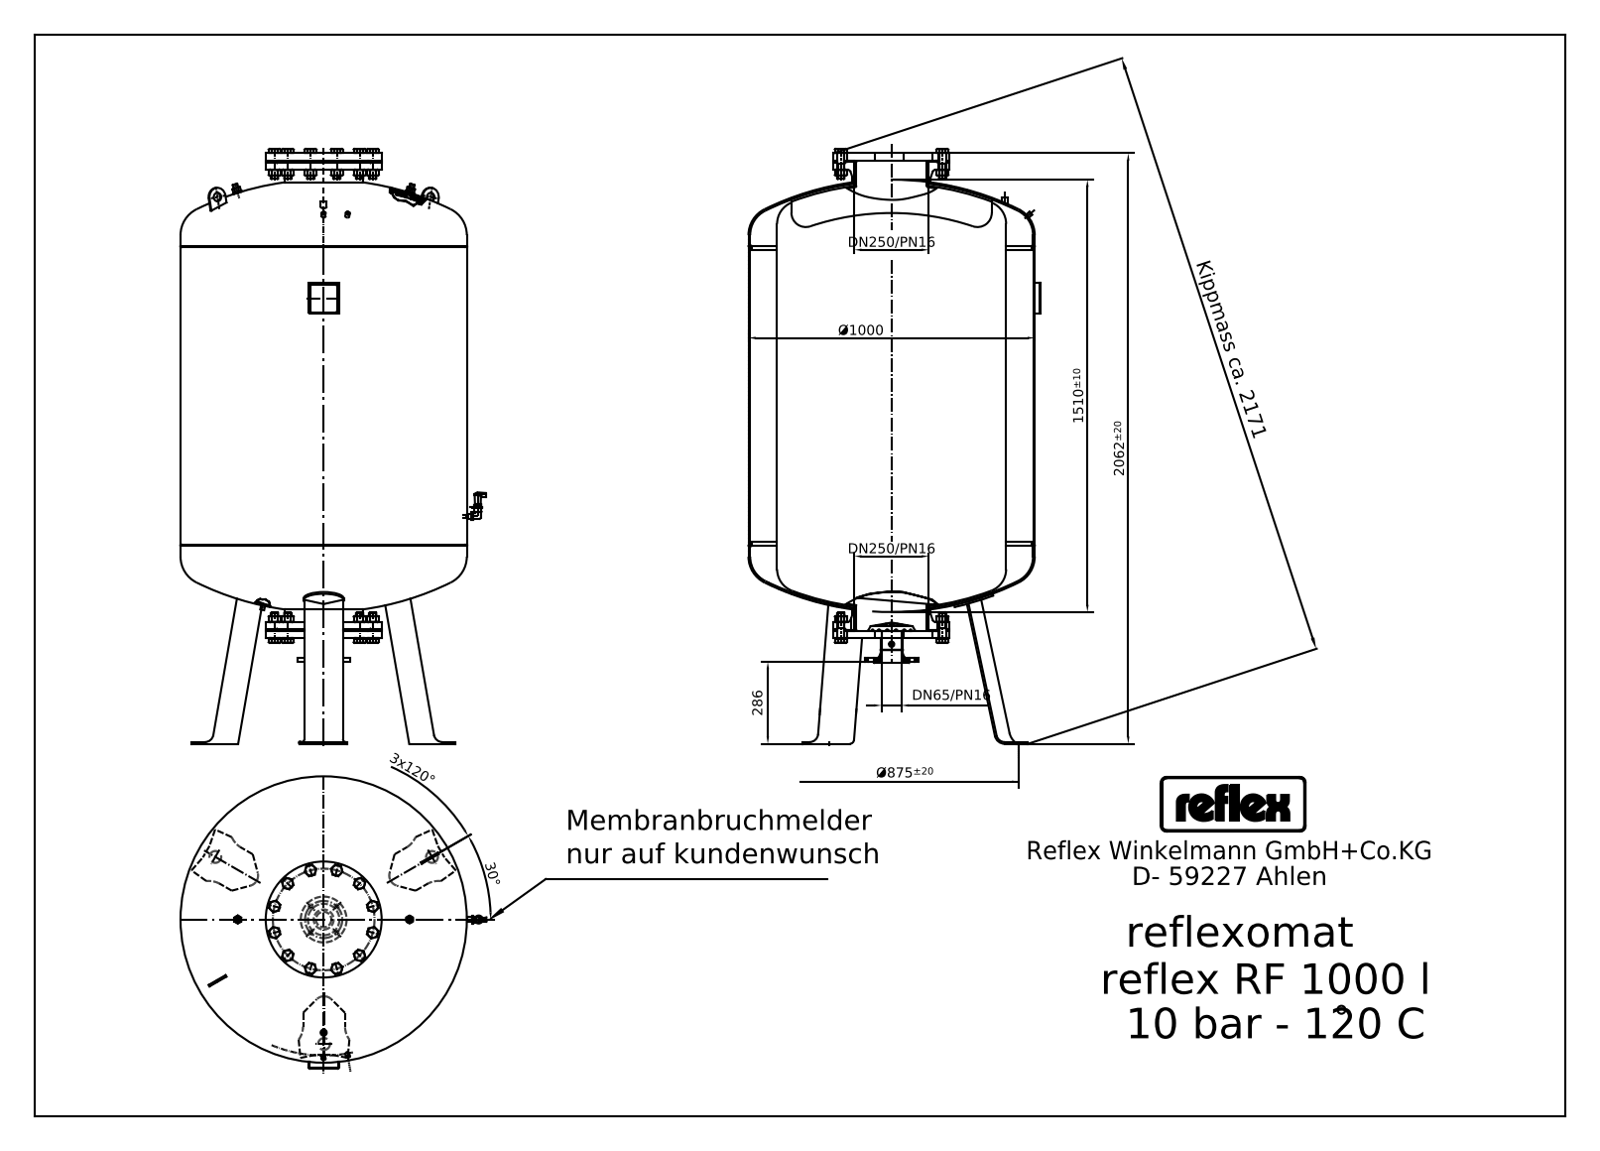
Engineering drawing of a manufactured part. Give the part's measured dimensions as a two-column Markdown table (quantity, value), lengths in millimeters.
| quantity | value |
| --- | --- |
| STEP written by | Mechanical Desktop 2009 (CONFIG_CONTROL_DESIGN) |
| units | millimeters |
| bodies | 23 solids, 940 faces (556 planar, 222 cylindrical, 162 other) |
| overall size | 2060 × 1066 × 1020 |
| volume | 1 092 000 000 mm³ |
| surface area | 10 700 000 mm² |
| round holes (diameter × count) | 11.45 × 2, 3.5 × 1, 14.95 × 1, 30 × 1, 260.4 × 1 |
| round bosses / shafts (diameter × count) | 16 × 12, 21.3 × 3, 18.5 × 3, 28 × 2, 20 × 2, 1000 × 1, 375 × 1, 273 × 1 |
| partial cylindrical surfaces (radius × count) | 25 × 18, 1 × 5, 8.44 × 4, 3.38 × 3, 6 × 3, 9 × 3, 2 × 2, 3 × 2 |
| main face-to-face distances | 1075, 22, 1664, 27, 1637, 1350.5, 275.5, 1372.5, 297.5, 313.5 |
| hole center spacings | 395, 519.5, 652.61 |
